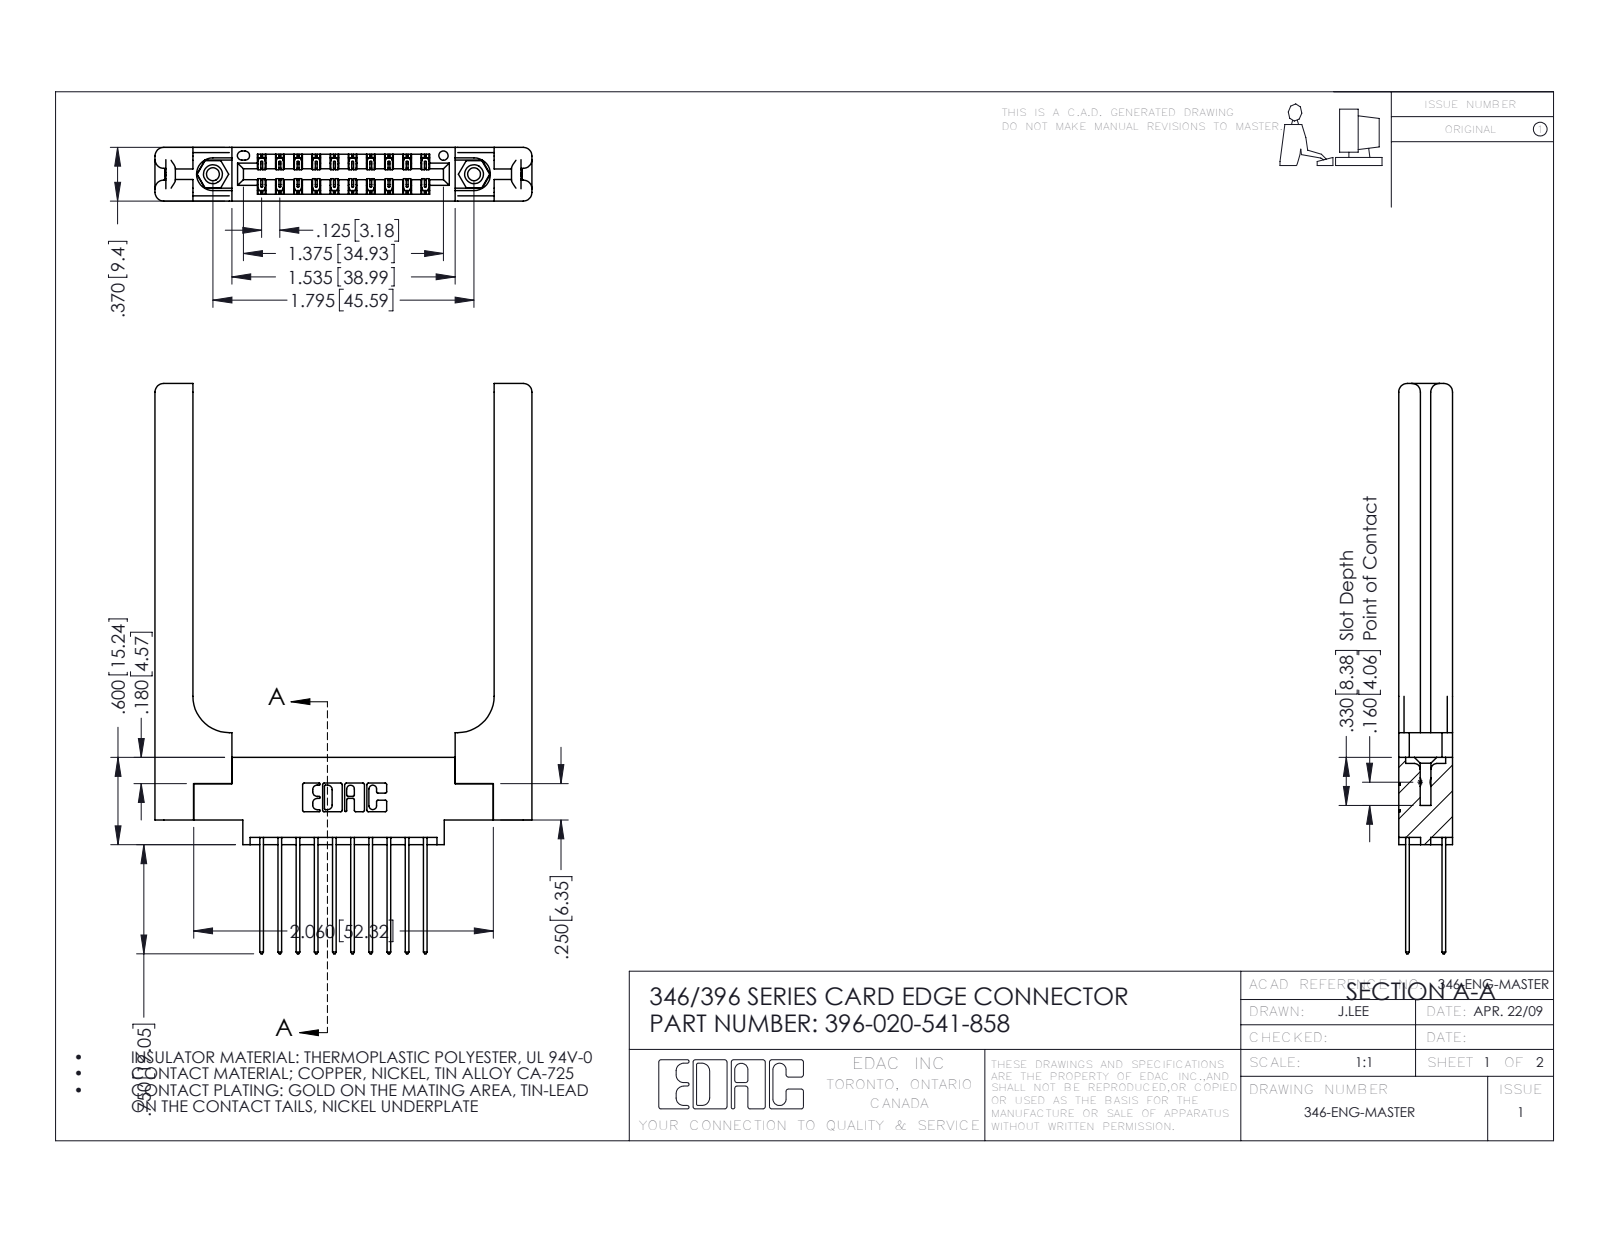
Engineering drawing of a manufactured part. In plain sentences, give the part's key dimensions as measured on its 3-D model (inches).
The part is named "345-250-001_345-250-001-102; 396-020-541-858; 346 Part_0.170 Offset - 0.156 Dia-TH; 346-220-058_345-220-058 (+1 more)". Its 3-D file was written by "SolidWorks 2016 (CONFIG_CONTROL_DESIGN)". It is 25 solids with 1422 faces: 928 planar, 434 cylindrical and 60 other. Overall it measures 3.92 by 2.591 by 0.37 inches. Its volume is 0.831 cubic inches and its surface area 21.12 square inches. Round holes: 2 of diameter 0.089, 2 of diameter 0.125, 2 of diameter 0.156, 1 of diameter 0.064. Round bosses or shafts: 2 of diameter 0.155. Partial cylindrical surfaces (rounded edges, fillets, slot ends): 30 of radius 0.006, 22 of radius 0.01, 20 of radius 0.01, 16 of radius 0.06, 6 of radius 0.007, 6 of radius 0.031, 3 of radius 0.026, 2 of radius 0.014. The main face-to-face distances are 0.37, 0.15, 0.072, 0.148, 0.048, 0.322, 0.25, 0.102, 0.22, 0.173. The hole center spacings are 0.246, 1.59, 1.795.
